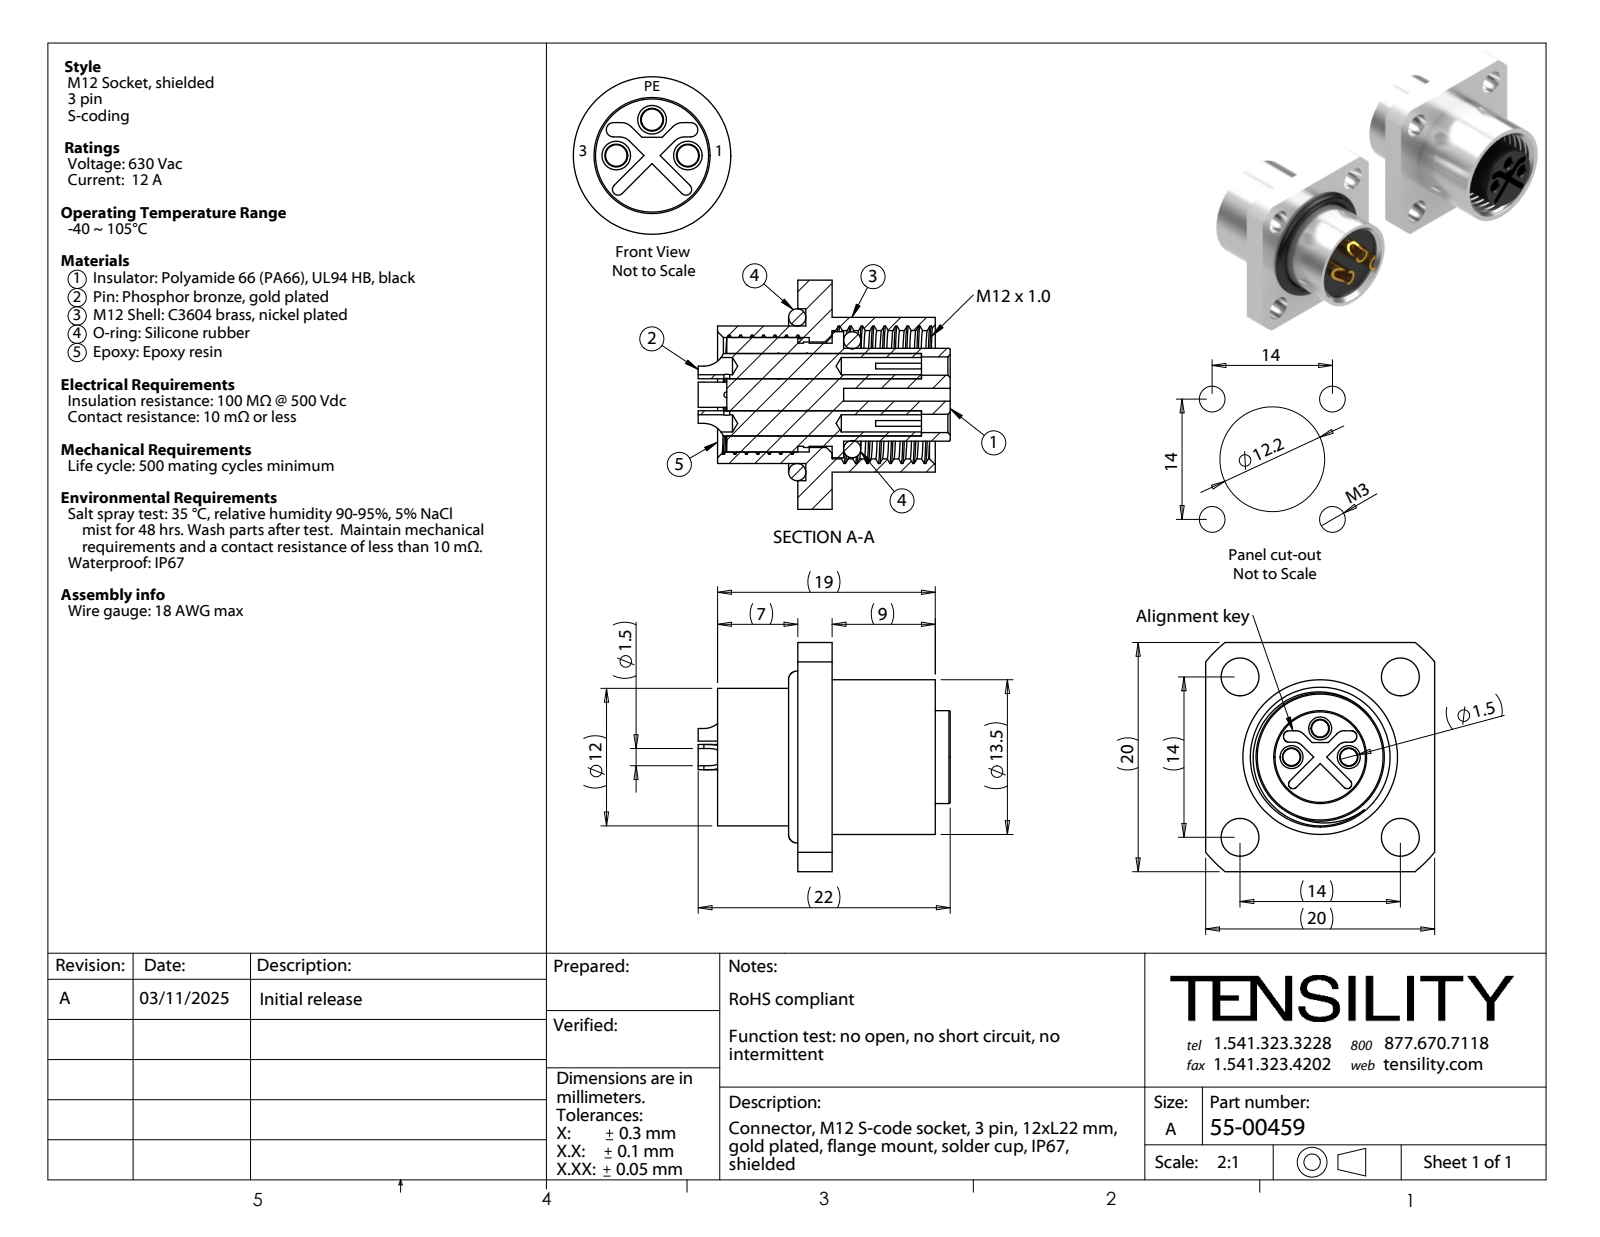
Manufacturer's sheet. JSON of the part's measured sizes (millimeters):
{"part_name": "55-00459-02; 55-00459-04; 55-00459-03; 55-00459 (+2 more)", "step_written_by": "SolidWorks 2021 (CONFIG_CONTROL_DESIGN)", "units": "millimeters", "bodies": {"solids": 7, "faces": 254, "planar": 75, "cylindrical": 124, "other": 55}, "overall_size": [22, 20, 20], "volume_mm3": 2646, "surface_area_mm2": 4744, "round_holes": [[3.3, 4], [1.5, 3], [1.6, 3], [0.5, 2], [9, 1], [9.2, 1], [10, 1], [11.2, 1], [15, 1]], "round_bosses_or_shafts": [[2.2, 3], [13.5, 1], [12, 1], [11, 1], [8.1, 1]], "partial_cylinders_radius": [[1, 4], [1.86, 3], [0.4, 2], [0.5, 2], [13, 1]], "face_to_face_distances": [3, 20, 0.8, 1, 9.2, 6.2, 6.9, 0.7, 2.3, 4], "hole_center_spacings": [8.32, 11.8, 9.9, 14, 2.5, 3.54, 19.8, 5]}
